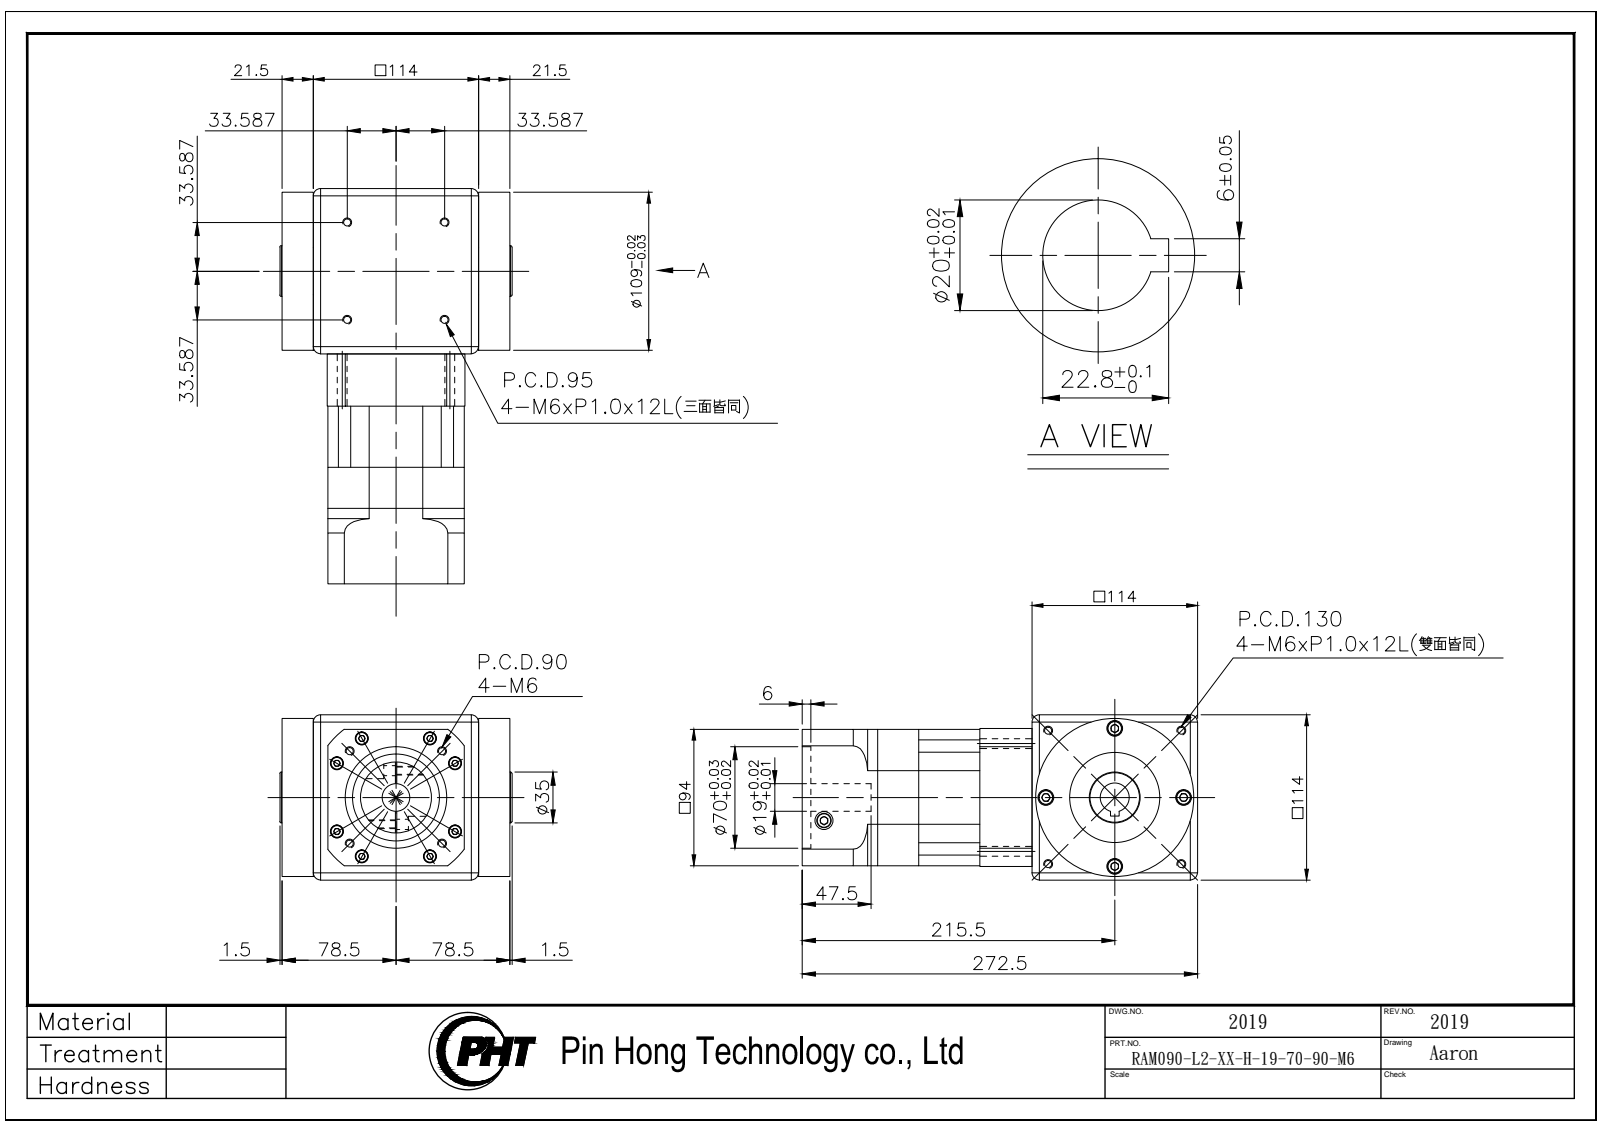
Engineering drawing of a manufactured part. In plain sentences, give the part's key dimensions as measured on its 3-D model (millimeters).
The part is named "RAM090-L2-XX-H-19-70-90-M6_2019". Its 3-D file was written by "SolidWorks 2016 (AUTOMOTIVE_DESIGN)". It is 4 solids with 645 faces: 301 planar, 228 cylindrical and 116 other. Overall it measures 272.5 by 160 by 114 millimeters. Its volume is 3 004 000 cubic millimeters and its surface area 255 140 square millimeters. Round holes: 16 of diameter 5, 8 of diameter 5.2, 8 of diameter 9, 4 of diameter 6.6, 4 of diameter 6.8, 4 of diameter 11, 2 of diameter 12.7, 1 of diameter 19, 1 of diameter 20, 1 of diameter 20.6, 1 of diameter 60, 1 of diameter 70. Round bosses or shafts: 8 of diameter 10, 8 of diameter 8.5, 1 of diameter 109, 1 of diameter 80, 1 of diameter 62, 1 of diameter 49, 1 of diameter 35. Partial cylindrical surfaces (rounded edges, fillets, slot ends): 4 of radius 6, 1 of radius 50.5, 1 of radius 59, 1 of radius 79.1. The main face-to-face distances are 114, 10, 104, 106.5, 28.3, 78.2, 220.5, 192.2, 94, 125.5. The hole center spacings are 47, 67.18, 12.17, 12.34, 14.08, 45.99, 47.5, 56.03.
